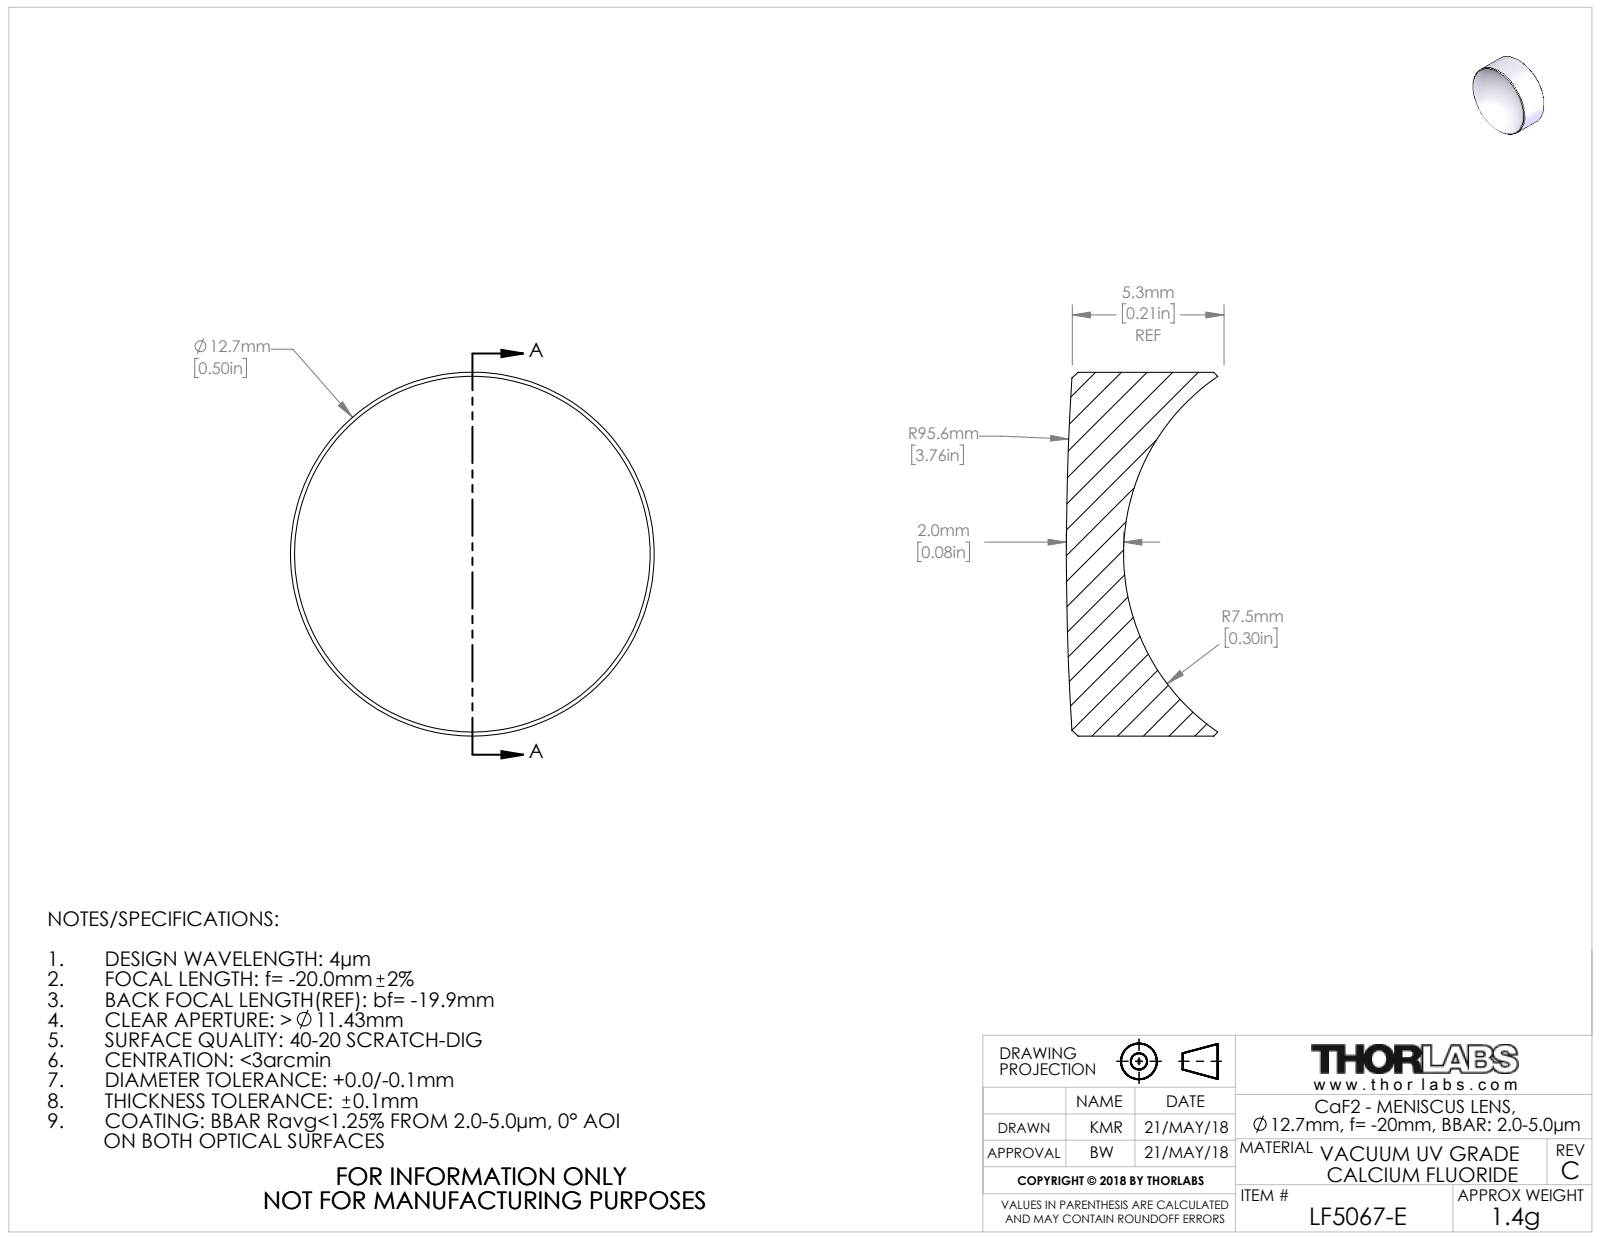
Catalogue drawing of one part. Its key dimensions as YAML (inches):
part_name: "20181-E0W"
step_written_by: "SolidWorks 2016 (CONFIG_CONTROL_DESIGN)"
units: inches
bodies: {solids: 1, faces: 10, planar: 0, cylindrical: 2, other: 8}
overall_size: [0.5, 0.5, 0.208]
volume: 0.027
surface_area: 0.748
round_bosses_or_shafts:
  - {diameter: 0.5, count: 1}
